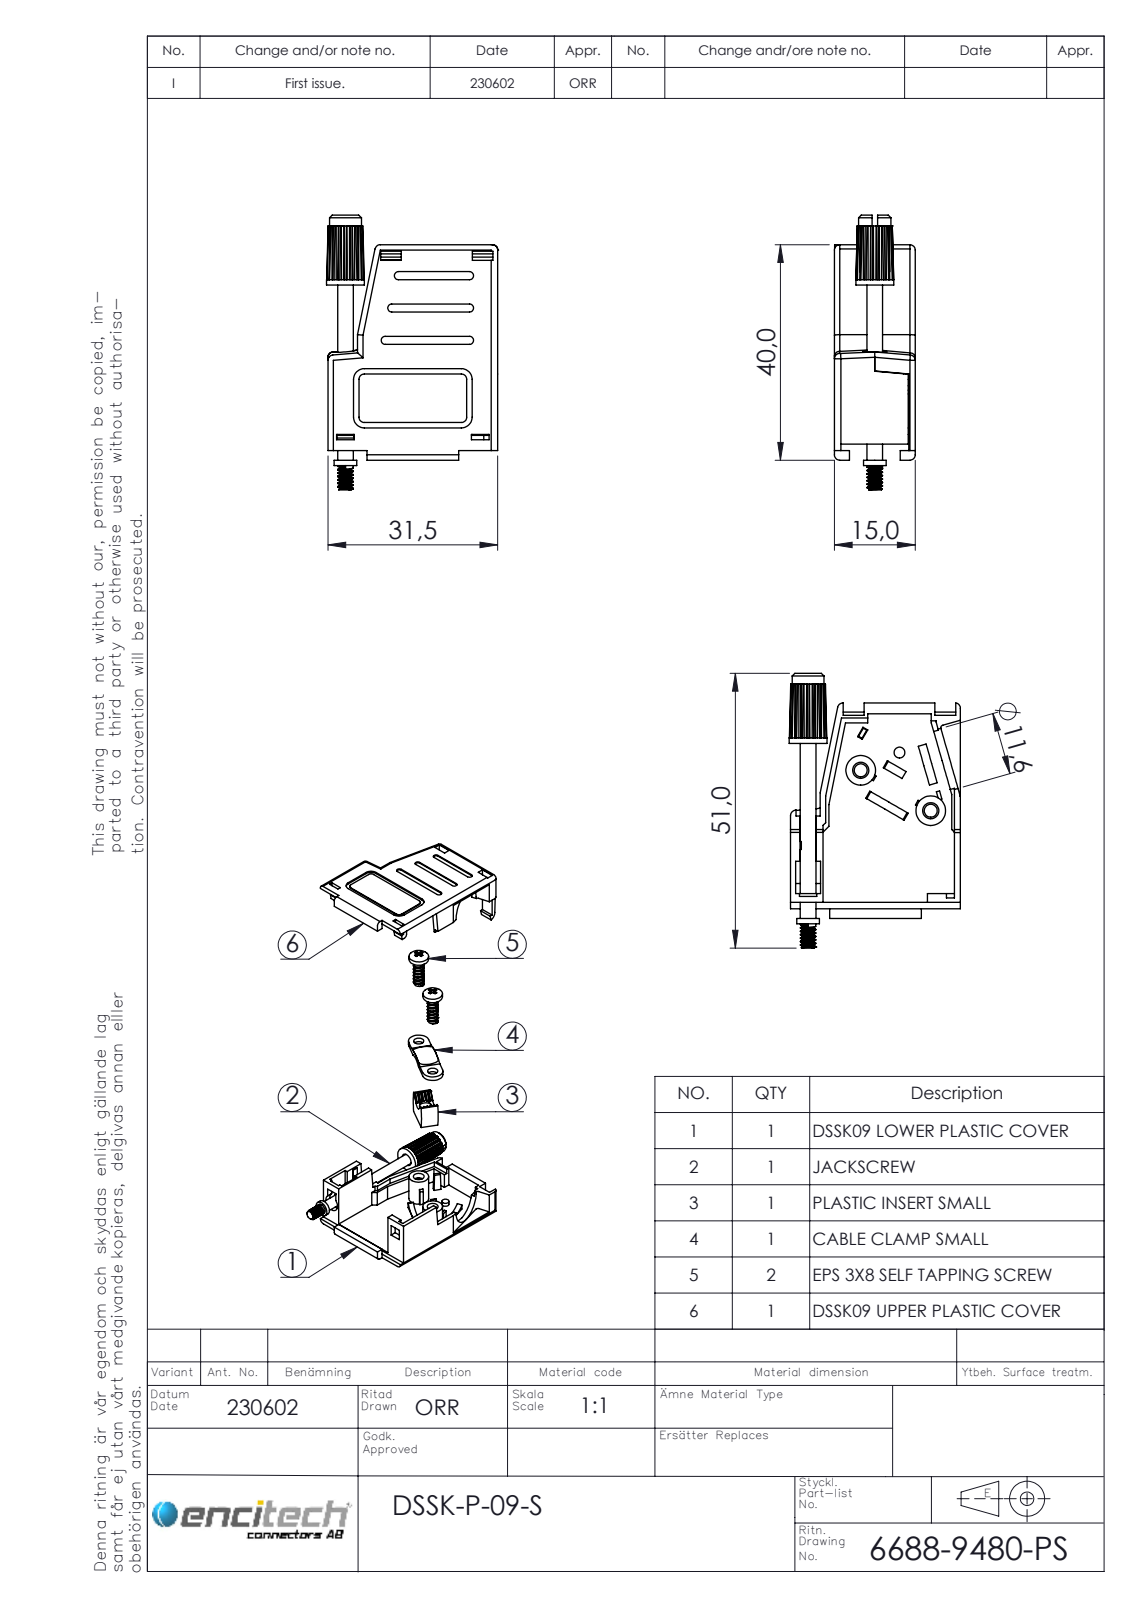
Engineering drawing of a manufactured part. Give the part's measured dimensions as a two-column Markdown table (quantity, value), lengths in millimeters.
| quantity | value |
| --- | --- |
| part name | 6811-0141-12 Part 2; 6811-0141-12 Part 1; 6718-0101-01; 6830-0106-01 (+3 more) |
| STEP written by | SolidWorks 2021 (AUTOMOTIVE_DESIGN) |
| units | millimeters |
| bodies | 9 solids, 735 faces (500 planar, 168 cylindrical, 67 other) |
| overall size | 51 × 31.75 × 15 |
| volume | 7 092 mm³ |
| surface area | 10 481 mm² |
| round holes (diameter × count) | 2.4 × 2, 2.8 × 2, 3 × 2, 3.5 × 1, 4.5 × 1, 11.6 × 1 |
| round bosses / shafts (diameter × count) | 5.5 × 2, 5.45 × 2, 2.46 × 2, 7 × 1, 6 × 1, 4.2 × 1, 2.9 × 1, 2.85 × 1 |
| partial cylindrical surfaces (radius × count) | 1 × 21, 0.75 × 6, 2 × 6, 0.5 × 5, 1.2 × 3, 2.85 × 2, 13 × 2, 1.5 × 1 |
| main face-to-face distances | 1.7, 13.3, 11.6, 15, 1.5, 1.2, 5.8, 7.5, 7.3, 1.1 |
| hole center spacings | 7.48, 7.52, 15 |
